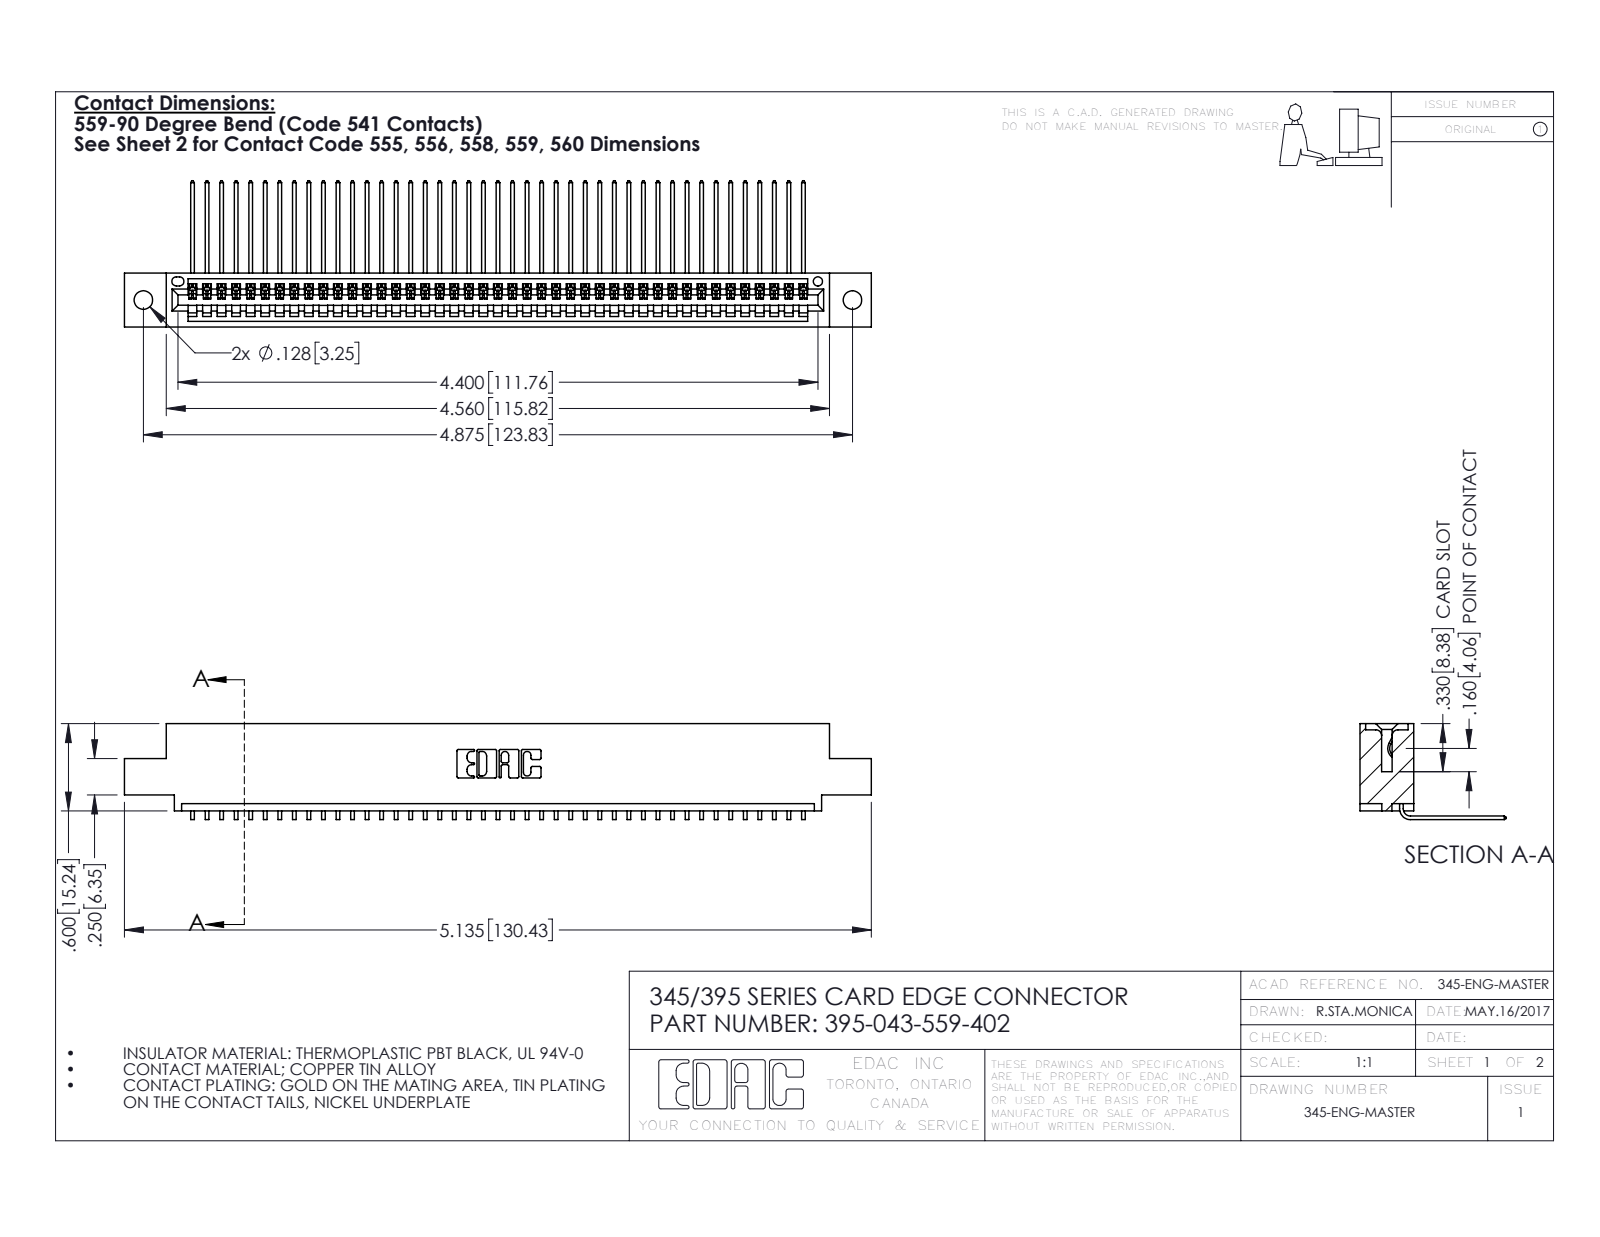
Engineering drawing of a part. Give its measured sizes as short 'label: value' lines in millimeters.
name: 345 Part_0.110 Offset - 0.128 Dia; 345-292-001_558 559 Tail - 1; 395-043-559-402
written by: SolidWorks 2016 (CONFIG_CONTROL_DESIGN)
unit: mm
bodies: 44 solids, 2710 faces (1890 planar, 820 cylindrical, 0 other)
size: 130.4 × 25.5 × 16.7
volume: 12 400 mm³; area: 17 180 mm²
holes: 2× ⌀3.3, 1× ⌀1.6
rounds: 86× R0.2, 22× R0.3, 6× R0.2, 6× R0.8, 3× R0.7, 2× R0.8, 2× R1, 1× R0.4
face distances: 1.8, 7.6, 9.4, 5.1, 2.5, 6.9, 0.6, 5.7, 3.8, 1.8
hole spacings: 6.9, 117.8, 123.8
